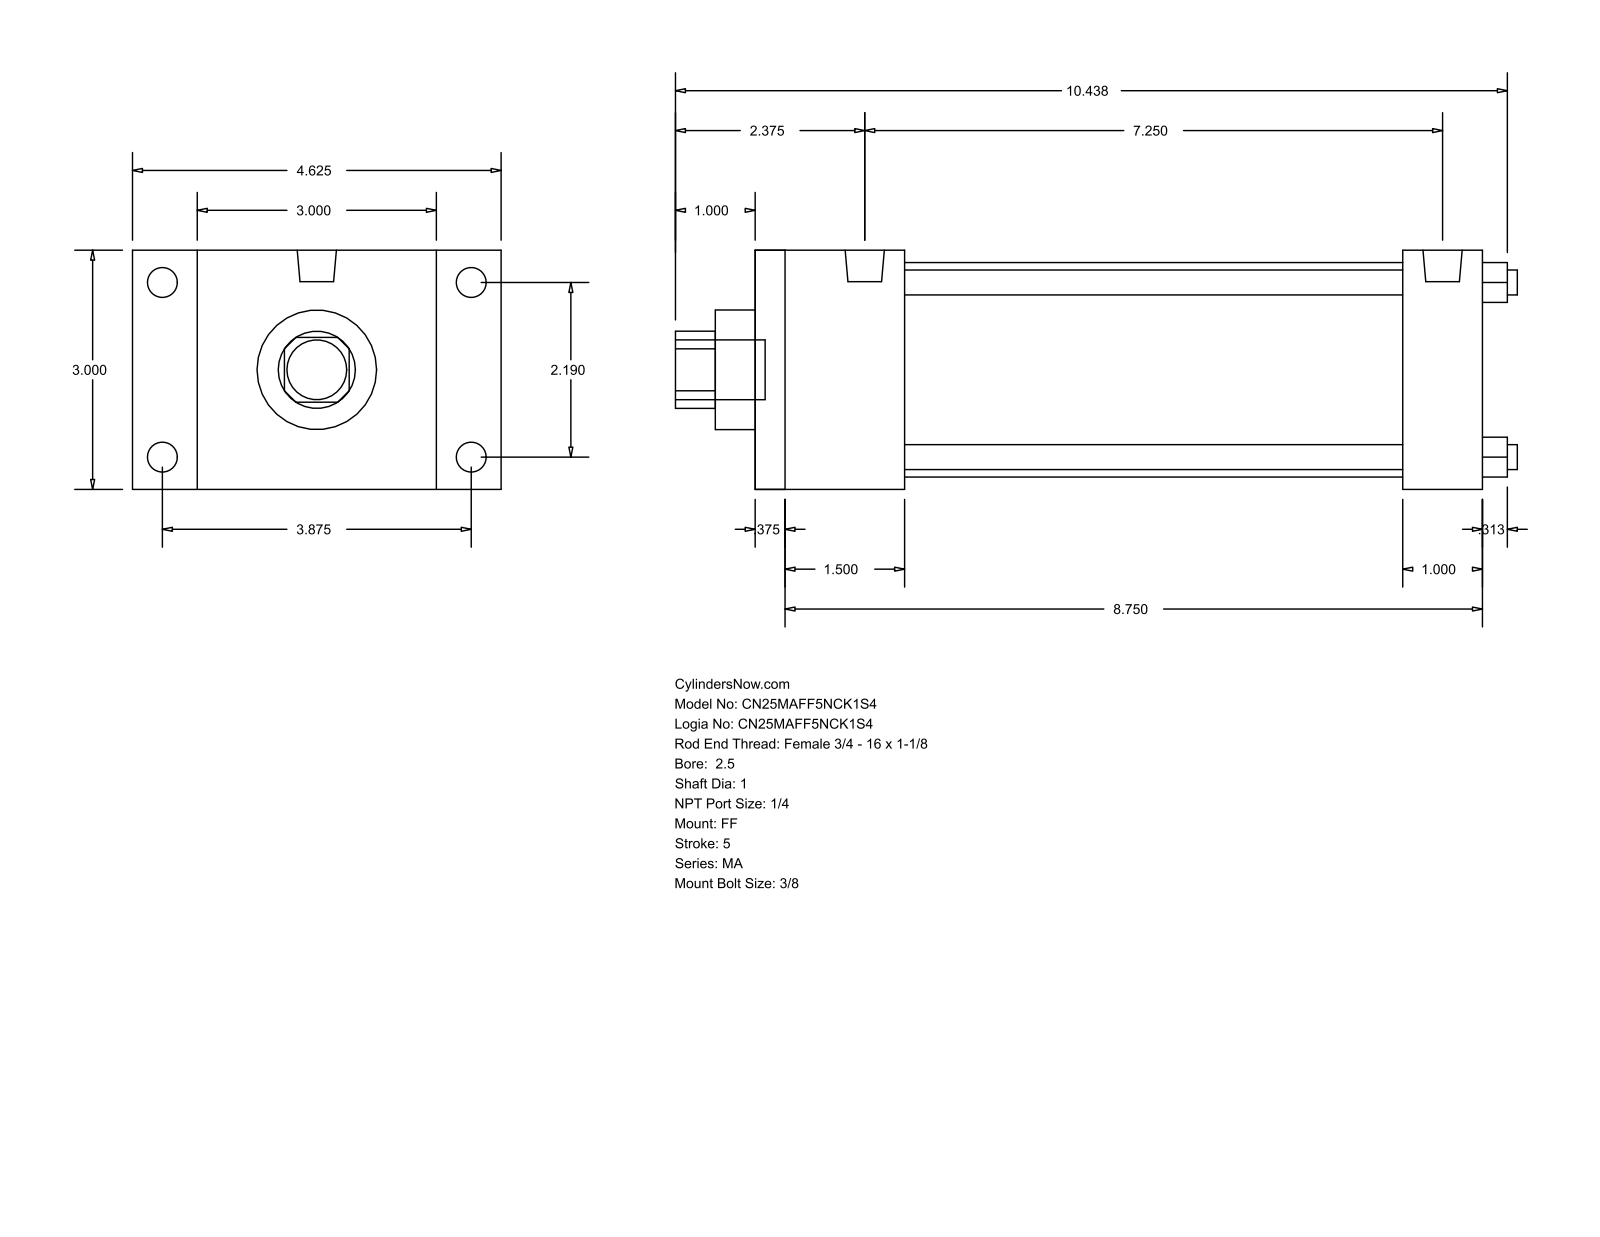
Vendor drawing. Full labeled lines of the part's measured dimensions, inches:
Part name (STEP PRODUCT): MA_FF__0250_1
STEP written by: GSSL Pune (CONFIG_CONTROL_DESIGN)
Units: inches
Bodies: 0 solids, 92 faces (64 planar, 28 cylindrical, 0 other)
Overall size (bounding box): 10.563 × 4.625 × 3
Round holes (diameter × count): ⌀0.313 ×4, ⌀1 ×1, ⌀1.5 ×1, ⌀2.69 ×1
Round bosses / shafts (diameter × count): ⌀0.375 ×4, ⌀0.313 ×4, ⌀0.492 ×2, ⌀0.75 ×1
Partial cylindrical surfaces — rounded edges, fillets, slot ends (radius × count): R0.484 ×1
Main face-to-face distances: 3, 9.125, 0.375, 8.75, 1, 1.875, 8.125, 1.5, 7.75, 6.25
Hole centre spacings: 1.548, 2.19, 3.097
